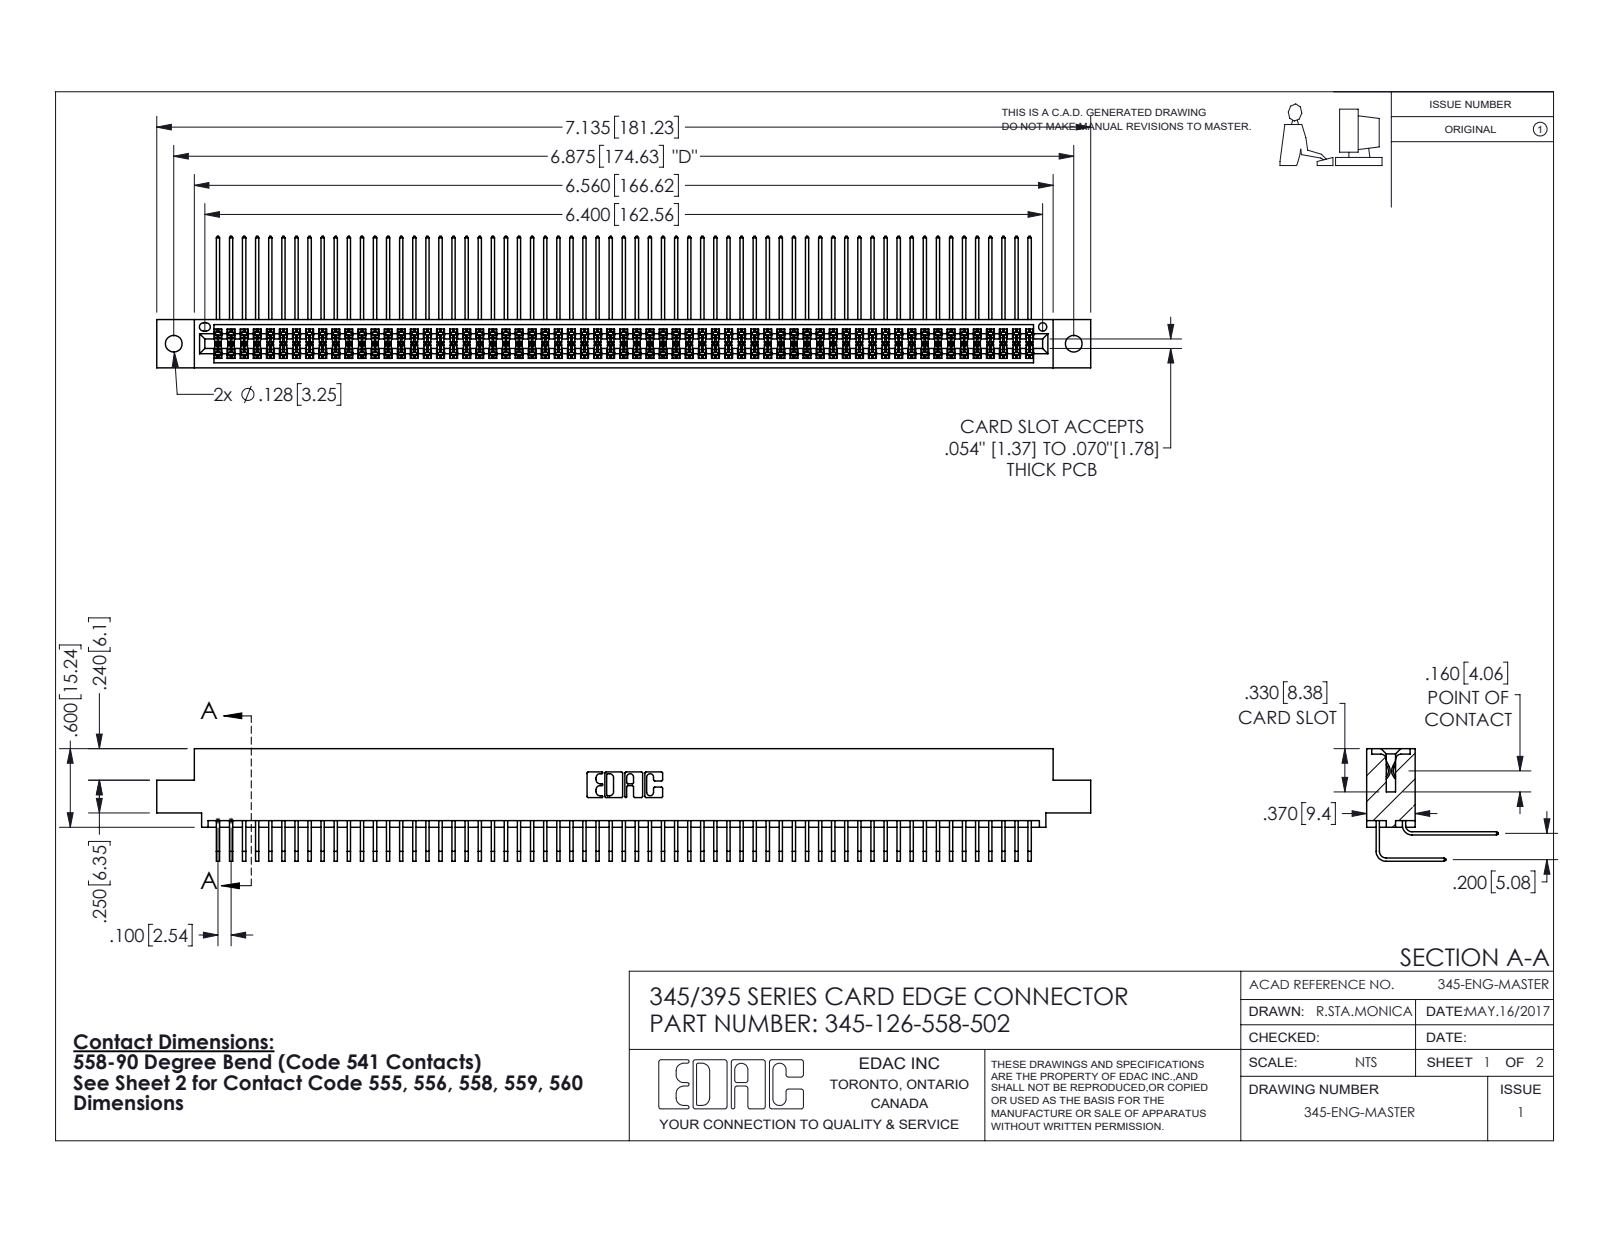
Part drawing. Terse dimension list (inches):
name: 345-126-558-502; 345-292-001_558 Tail - 2; 345-292-001_558 559 Tail - 1; 345 Part_0.110 Offset - 0.128 Dia
written by: SolidWorks 2016 (CONFIG_CONTROL_DESIGN)
unit: in
bodies: 127 solids, 6682 faces (4494 planar, 2188 cylindrical, 0 other)
size: 7.135 × 1.005 × 0.859
volume: 1.124 in³; area: 47.84 in²
holes: 2× ⌀0.128, 1× ⌀0.064
rounds: 252× R0.006, 22× R0.01, 6× R0.007, 6× R0.031, 3× R0.026, 2× R0.014, 2× R0.019, 2× R0.022
face distances: 0.072, 0.298, 0.2, 0.37, 0.098, 0.272, 0.025, 0.225, 0.025, 0.175
hole spacings: 0.27, 6.639, 6.875
